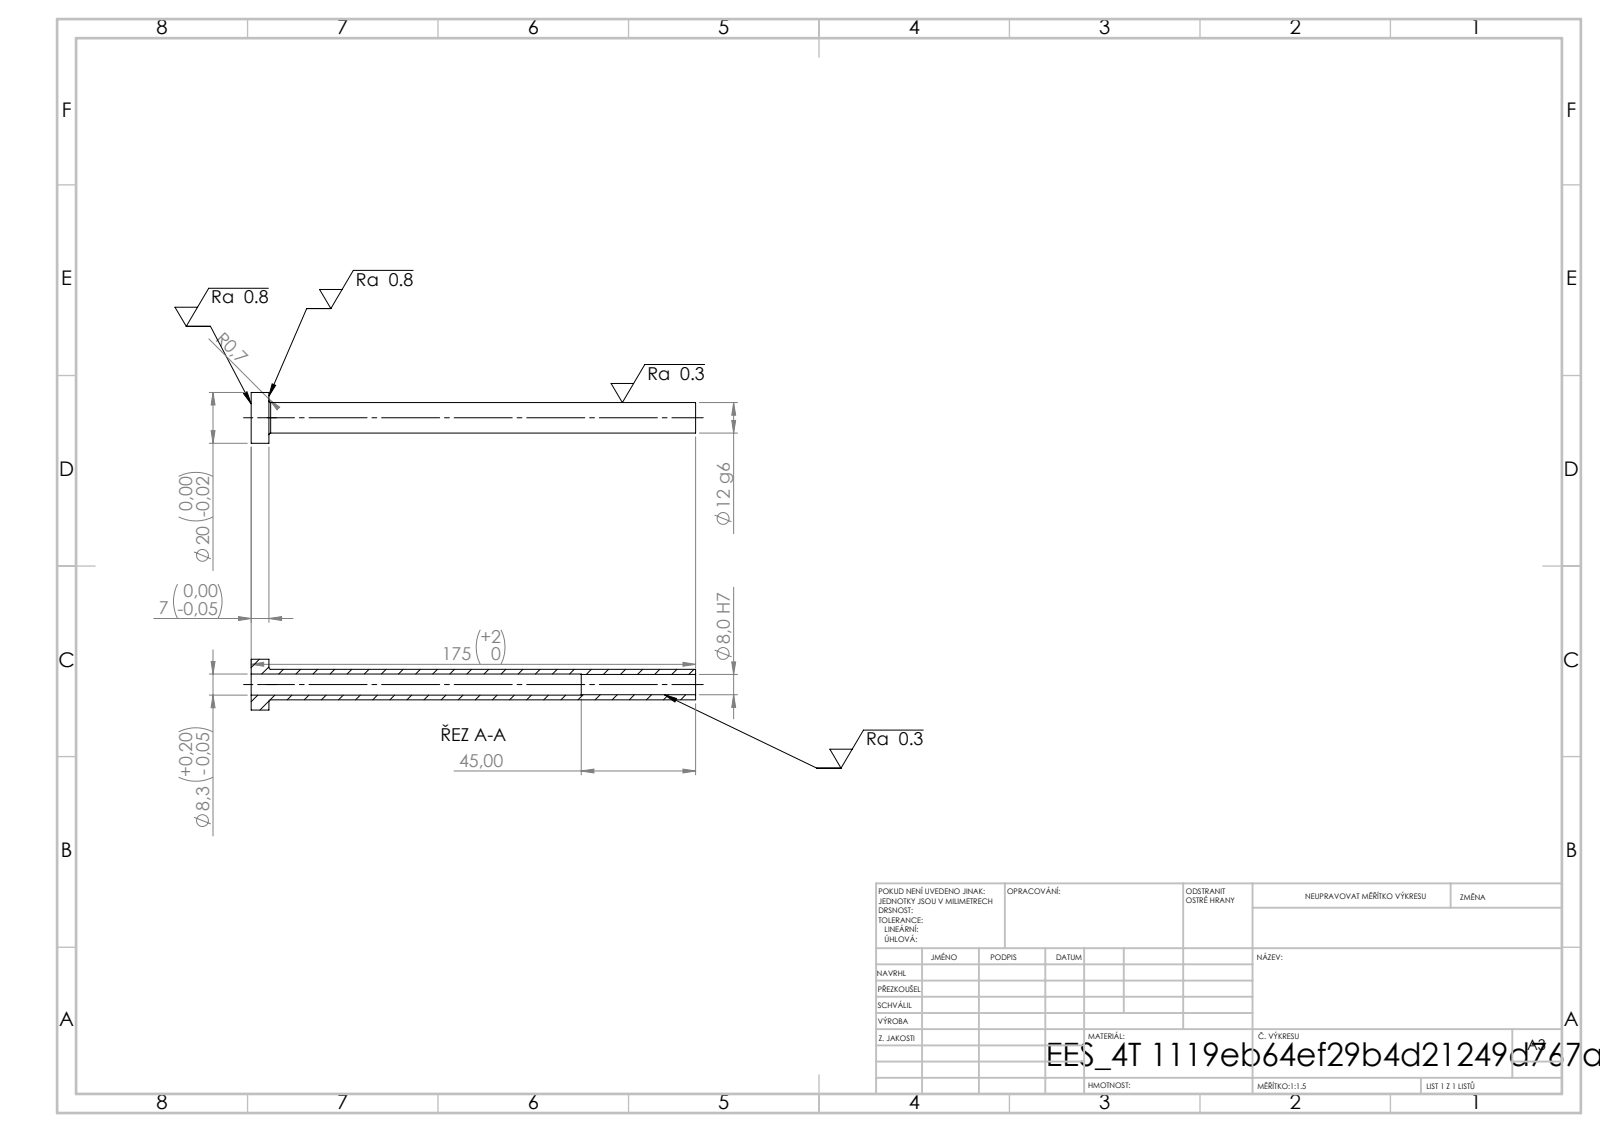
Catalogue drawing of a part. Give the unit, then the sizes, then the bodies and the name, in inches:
Units: inches
Overall size (bounding box): 6.89 × 0.787 × 0.787
Round holes (diameter × count): ⌀0.315 ×1, ⌀0.327 ×1
Round bosses / shafts (diameter × count): ⌀0.787 ×1, ⌀0.472 ×1
Main face-to-face distances: 0.276, 6.89, 6.614, 5.118, 4.843, 1.772
Volume: 0.727 in³ · Surface area: 18.31 in²
Bodies: 1 solid, 14 faces (4 planar, 8 cylindrical, 2 other)
STEP written by: SolidWorks 2019 (CONFIG_CONTROL_DESIGN)
